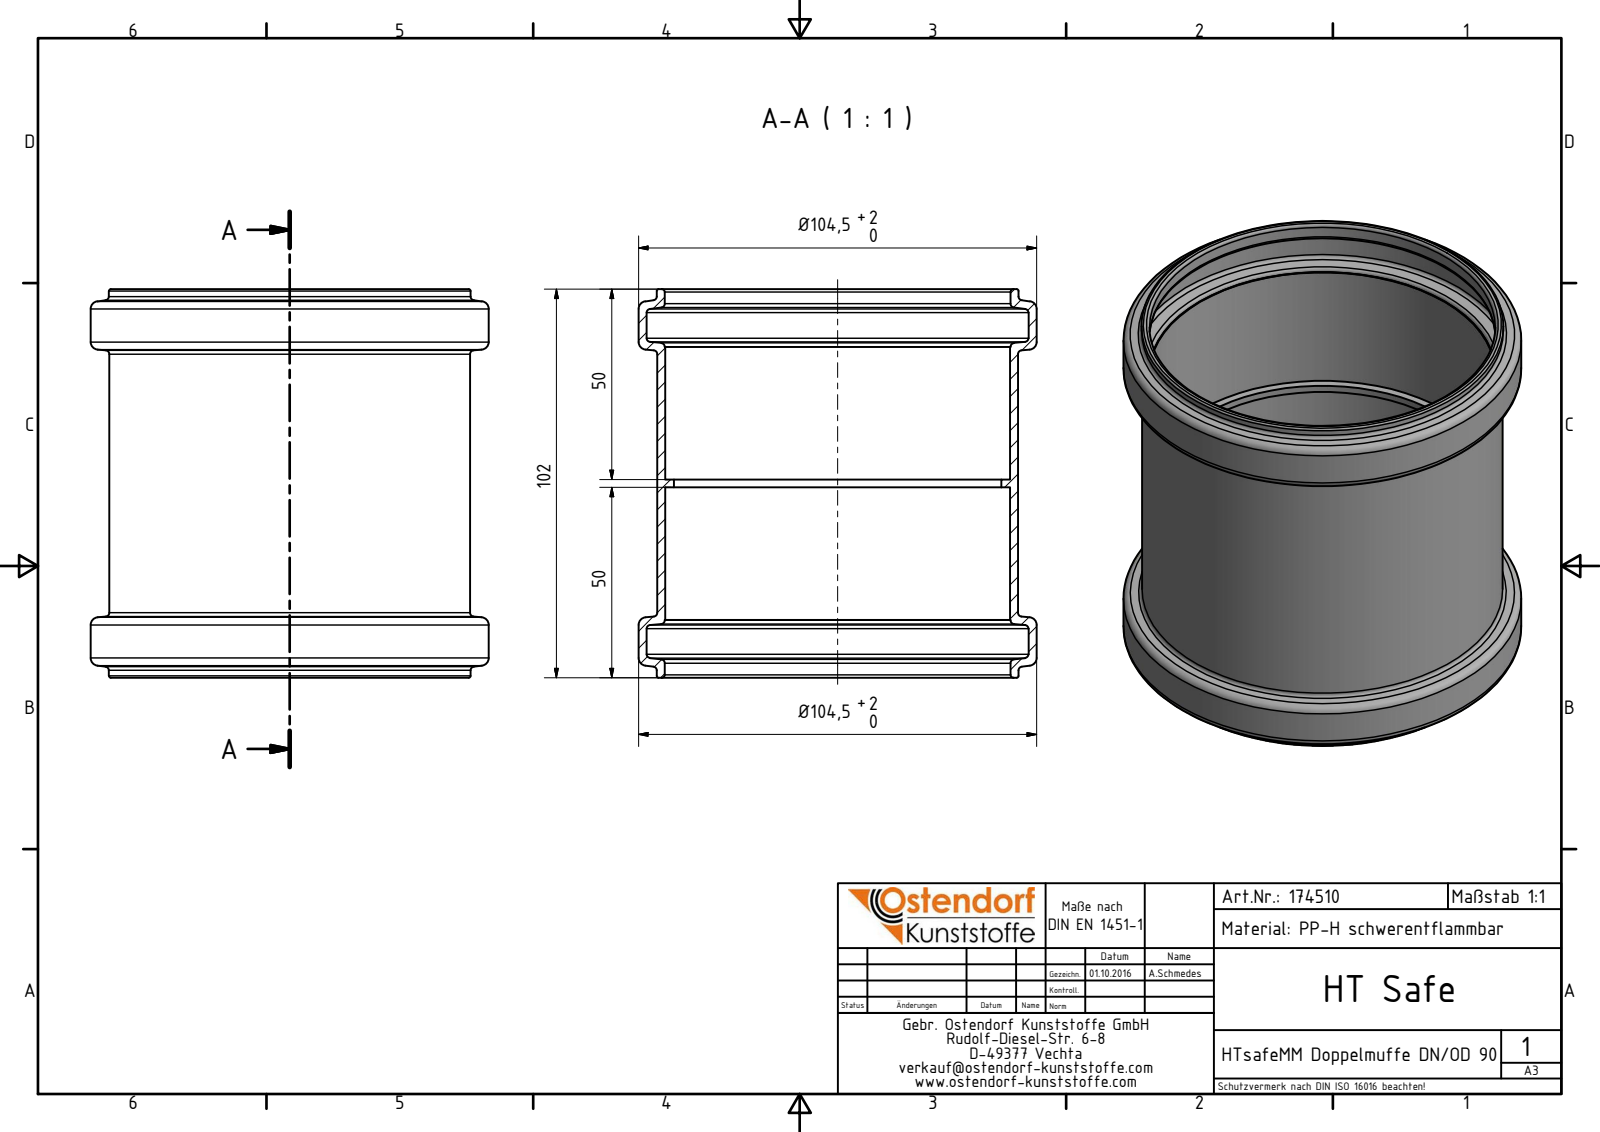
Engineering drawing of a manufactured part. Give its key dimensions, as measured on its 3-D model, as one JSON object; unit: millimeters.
{"part_name": "174510 HTsafeMM DN_OD 90", "step_written_by": "Autodesk Inventor 2016 (AUTOMOTIVE_DESIGN)", "units": "millimeters", "bodies": {"solids": 1, "faces": 48, "planar": 6, "cylindrical": 14, "other": 28}, "overall_size": [104.5, 104.5, 102], "volume_mm3": 75327, "surface_area_mm2": 71403, "round_holes": [[86, 1], [90.5, 1], [90.8, 1], [100.3, 1]], "round_bosses_or_shafts": [[104.5, 1], [95, 1], [94.7, 1]], "face_to_face_distances": [2, 50, 52, 102, 15.21, 86.79, 34.79, 36.79, 71.58]}
